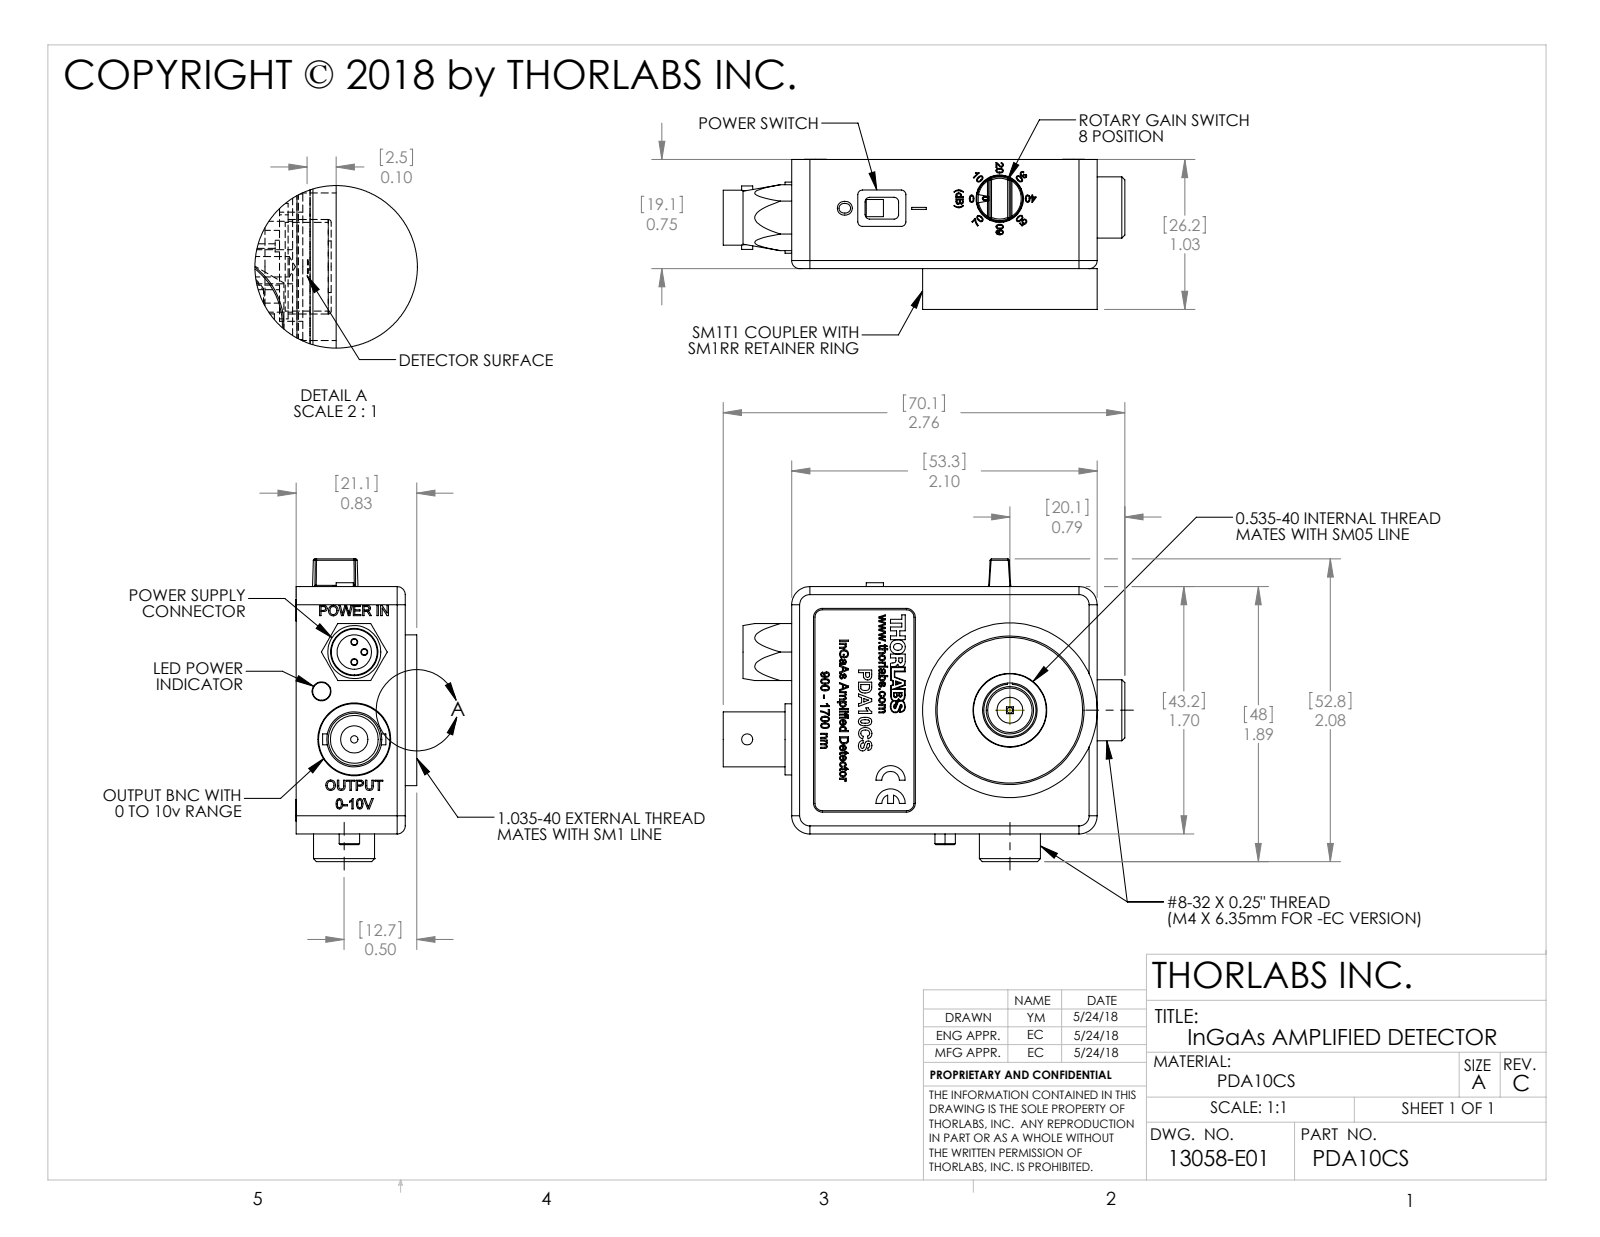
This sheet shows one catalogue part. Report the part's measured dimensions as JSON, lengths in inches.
{"part_name": "13058-E0W", "step_written_by": "SolidWorks 2011 (CONFIG_CONTROL_DESIGN)", "units": "inches", "bodies": {"solids": 0, "faces": 541, "planar": 347, "cylindrical": 90, "other": 104}, "overall_size": [2.761, 2.058, 1.082], "round_holes": [[0.039, 3], [0.136, 2], [0.05, 1], [0.13, 1], [0.177, 1], [0.315, 1], [0.325, 1], [0.328, 1], [0.375, 1], [0.385, 1], [0.507, 1], [1, 1]], "round_bosses_or_shafts": [[0.147, 4], [0.42, 2], [1.2, 1], [0.49, 1], [0.378, 1], [0.37, 1], [0.325, 1], [0.236, 1]], "partial_cylinders_radius": [[0.031, 8], [0.095, 8], [0.125, 6], [0.055, 4], [0.062, 3], [0.05, 2], [0.063, 1], [0.075, 1]], "face_to_face_distances": [0.565, 0.063, 0.502, 0.502, 0.439, 0.063, 0.298, 0.8, 0.737, 0.235], "hole_center_spacings": [0.069, 0.098, 0.112, 0.138, 0.202, 0.212, 0.286, 0.339]}
